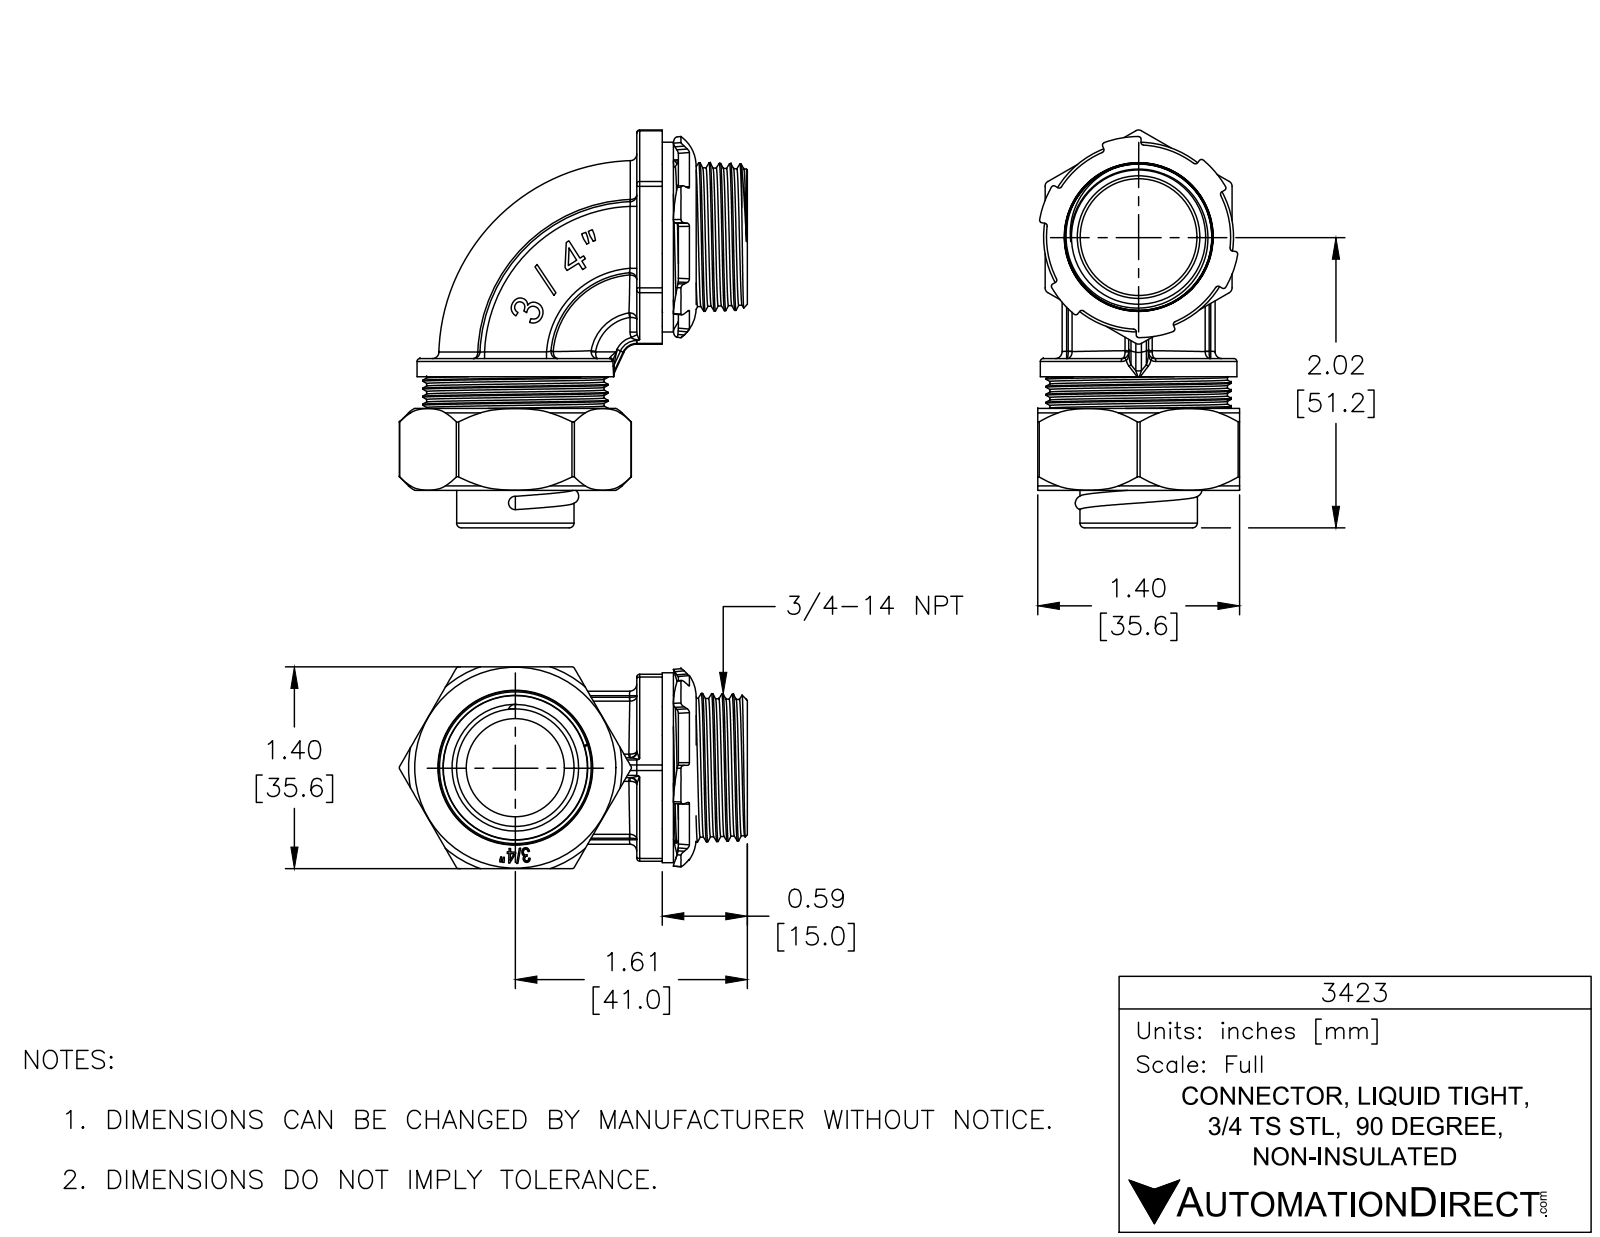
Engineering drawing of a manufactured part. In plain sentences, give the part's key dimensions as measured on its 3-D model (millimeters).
The part is named "3423-3; 3423-5; 3423-2; 3423 (+3 more)". Its 3-D file was written by "SolidWorks 2017 (AUTOMOTIVE_DESIGN)". It is 6 solids with 689 faces: 256 planar, 144 cylindrical and 289 other. Overall it measures 70.2 by 61.4 by 35.6 millimeters. Its volume is 24 450 cubic millimeters and its surface area 28 200 square millimeters. Round holes: 2 of diameter 22, 1 of diameter 3.2, 1 of diameter 17.3, 1 of diameter 19.1, 1 of diameter 20.6, 1 of diameter 23, 1 of diameter 26.3, 1 of diameter 27.1, 1 of diameter 27.3, 1 of diameter 28.4, 1 of diameter 31.9, 1 of diameter 33.3. Round bosses or shafts: 1 of diameter 34.7, 1 of diameter 33.5, 1 of diameter 32.7, 1 of diameter 30.8, 1 of diameter 28, 1 of diameter 20.7, 1 of diameter 19, 1 of diameter 2.6. Partial cylindrical surfaces (rounded edges, fillets, slot ends): 12 of radius 0.5, 12 of radius 1.2, 8 of radius 0.2, 7 of radius 1, 2 of radius 0.8, 1 of radius 0.1, 1 of radius 0.3, 1 of radius 0.4. The main face-to-face distances are 4.3, 31.3, 35.6, 20, 27, 2, 35.6, 23.2, 3.2, 6.5. The hole center spacings are 15.6.
